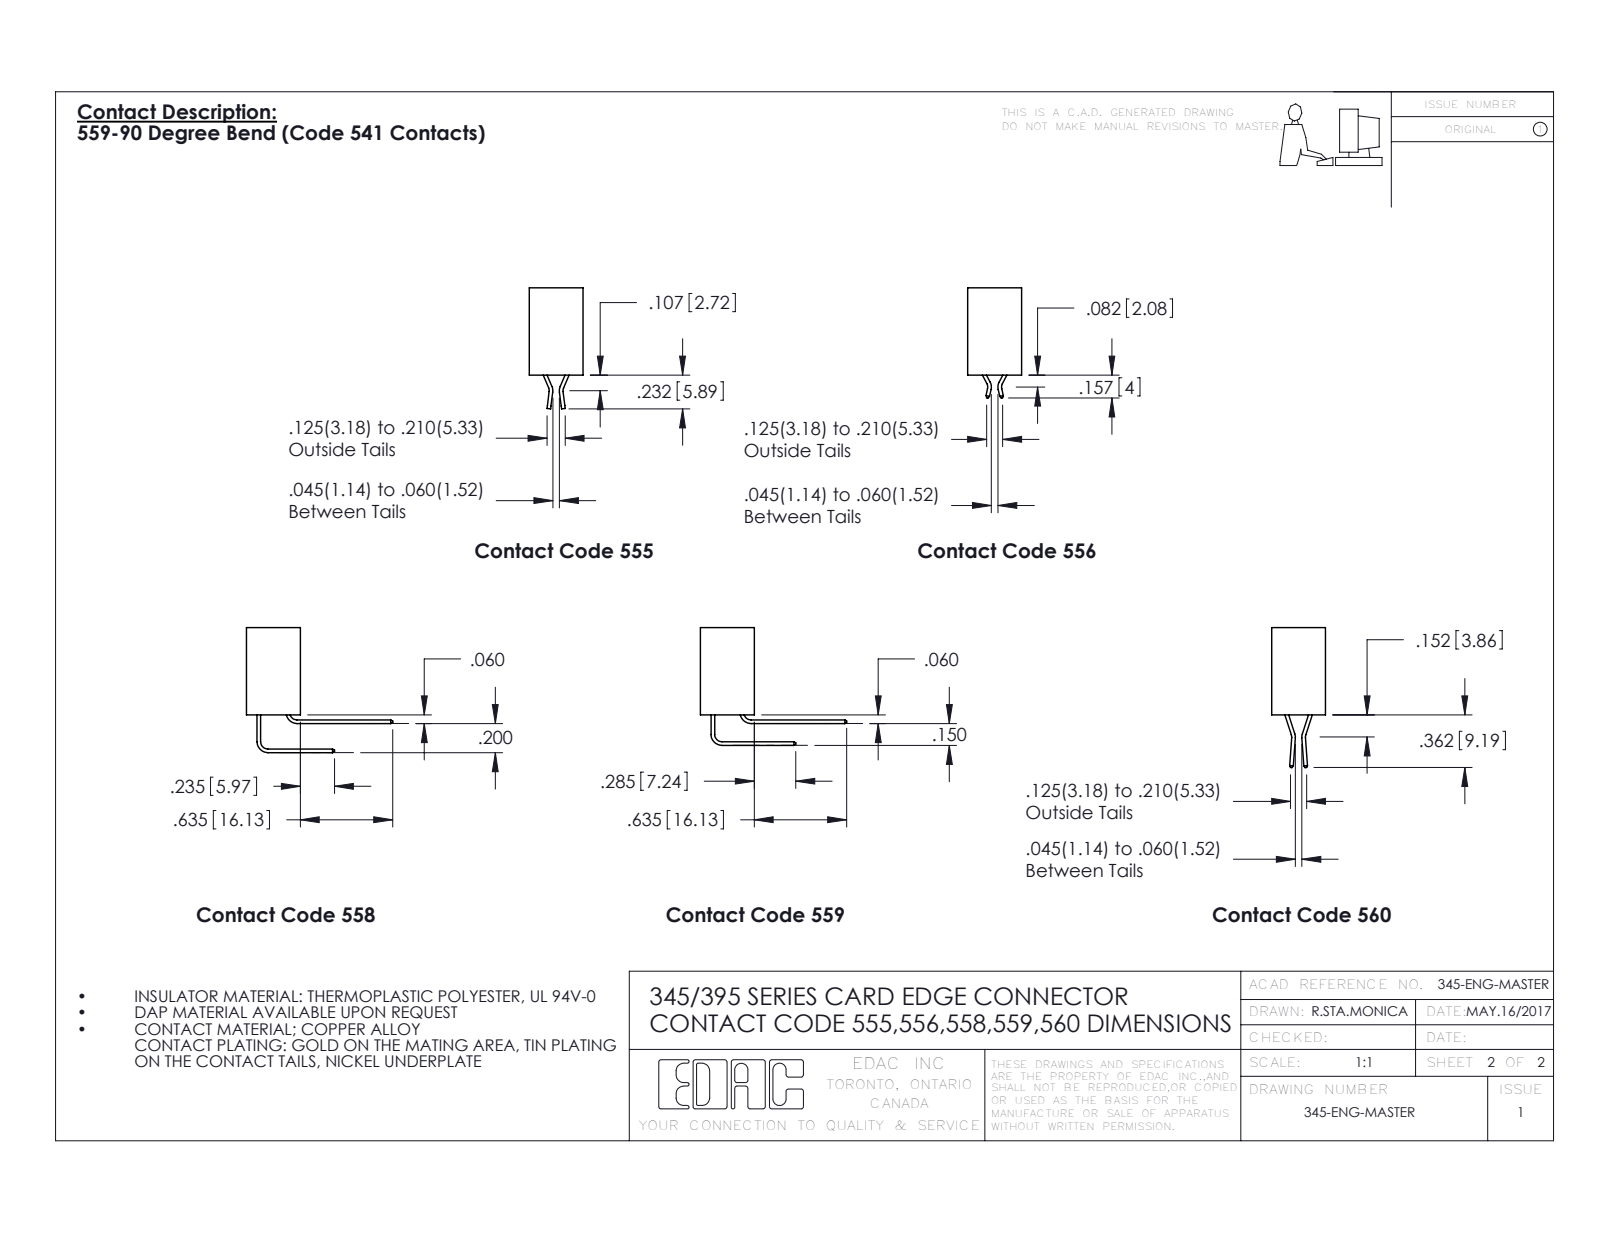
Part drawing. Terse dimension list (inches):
name: 395-005-559-104; 345-292-001_558 559 Tail - 1; 345 Part_Flush Mounting Lugs - 0.156 Dia-TH
written by: SolidWorks 2016 (CONFIG_CONTROL_DESIGN)
unit: in
bodies: 6 solids, 426 faces (290 planar, 136 cylindrical, 0 other)
size: 1.335 × 1.005 × 0.659
volume: 0.174 in³; area: 4.939 in²
holes: 2× ⌀0.156, 1× ⌀0.064
rounds: 22× R0.01, 10× R0.006, 6× R0.007, 6× R0.031, 3× R0.026, 2× R0.031, 2× R0.04, 1× R0.014
face distances: 0.2, 0.37, 0.1, 0.298, 0.072, 0.25, 0.06, 0.098, 0.272, 0.025
hole spacings: 0.27, 0.847, 1.075
